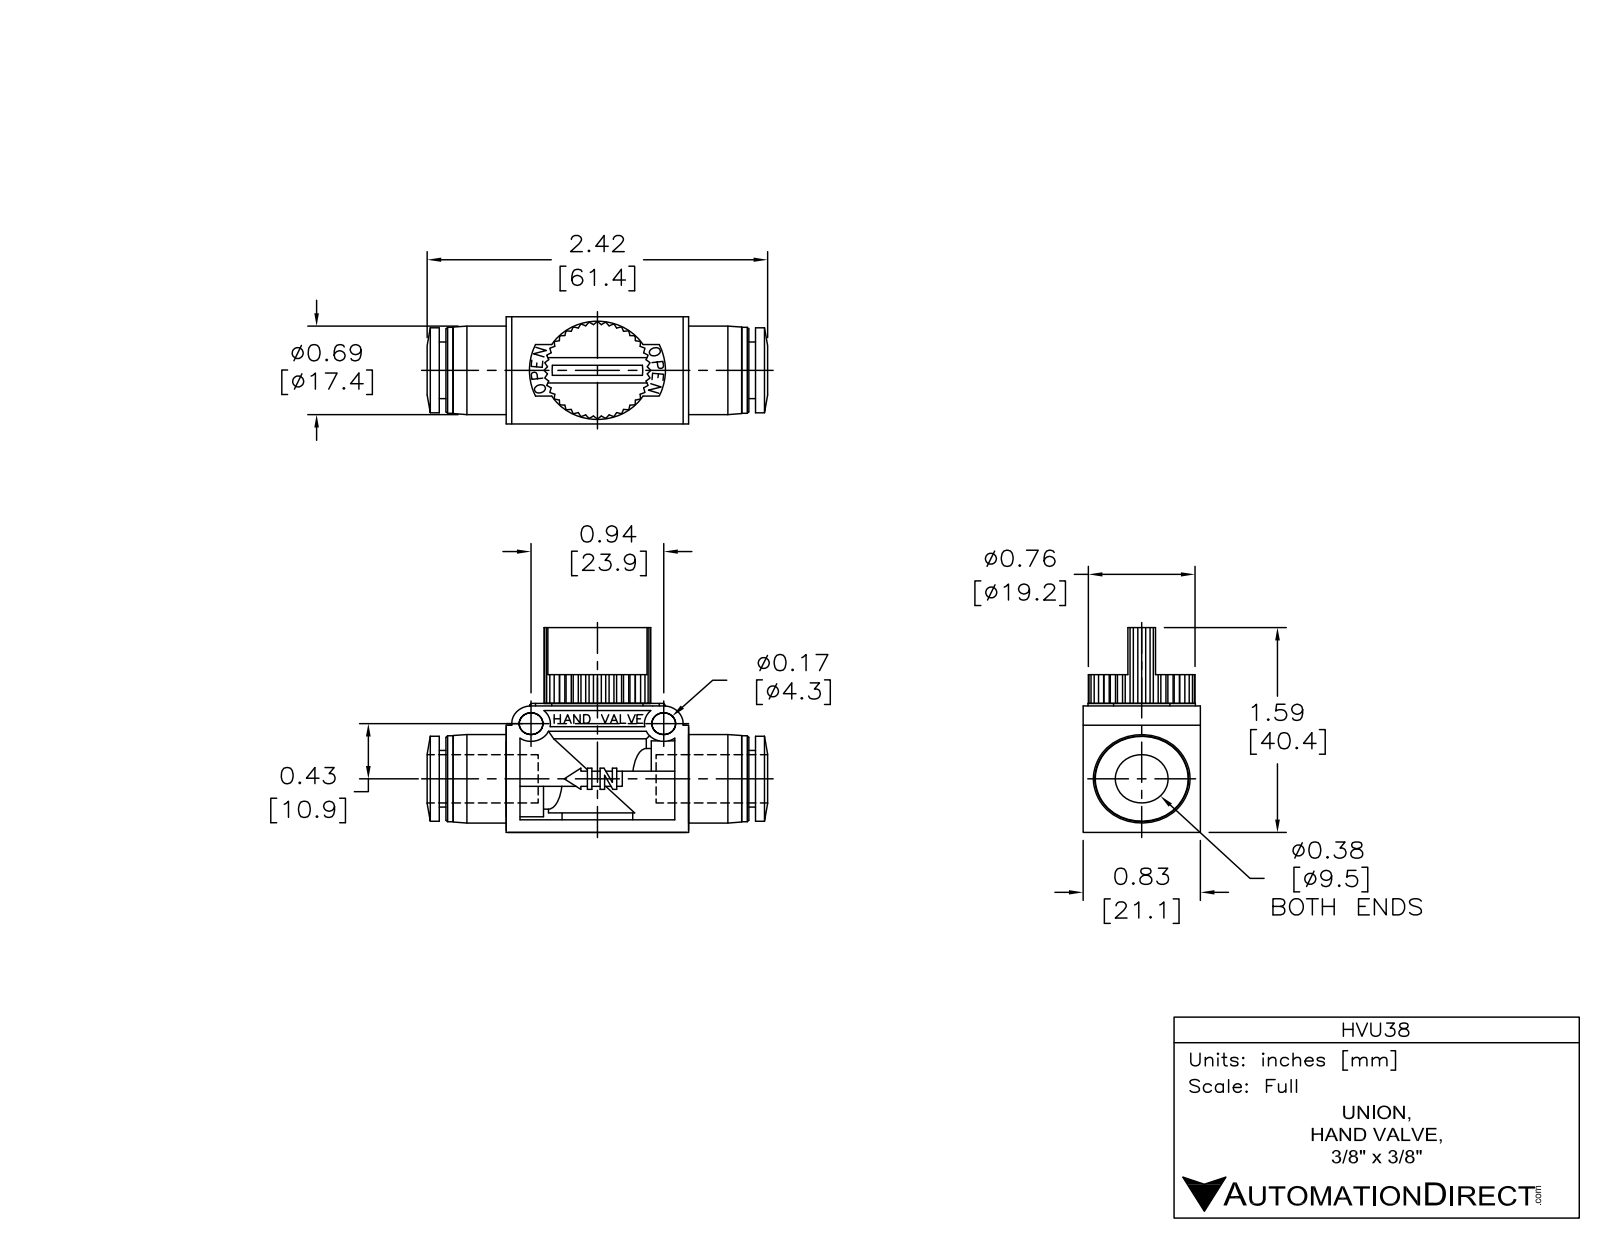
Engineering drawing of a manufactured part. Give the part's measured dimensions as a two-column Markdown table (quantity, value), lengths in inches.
| quantity | value |
| --- | --- |
| part name | HVU38 |
| STEP written by | SolidWorks 2015 (AUTOMOTIVE_DESIGN) |
| units | inches |
| bodies | 1 solid, 303 faces (212 planar, 60 cylindrical, 31 other) |
| overall size | 2.425 × 1.594 × 0.835 |
| volume | 1.15 in³ |
| surface area | 16.27 in² |
| round holes (diameter × count) | 0.169 × 2, 0.386 × 1 |
| round bosses / shafts (diameter × count) | 0.701 × 1, 0.697 × 1, 0.689 × 1, 0.669 × 1, 0.661 × 1, 0.591 × 1, 0.441 × 1 |
| partial cylindrical surfaces (radius × count) | 0.138 × 2, 0.24 × 1, 0.252 × 1, 0.407 × 1 |
| main face-to-face distances | 0.098, 0.319, 0.516, 0.476, 0.059, 0.378, 0.457, 0.835, 0.138, 0.528 |
| hole center spacings | 0.945 |
